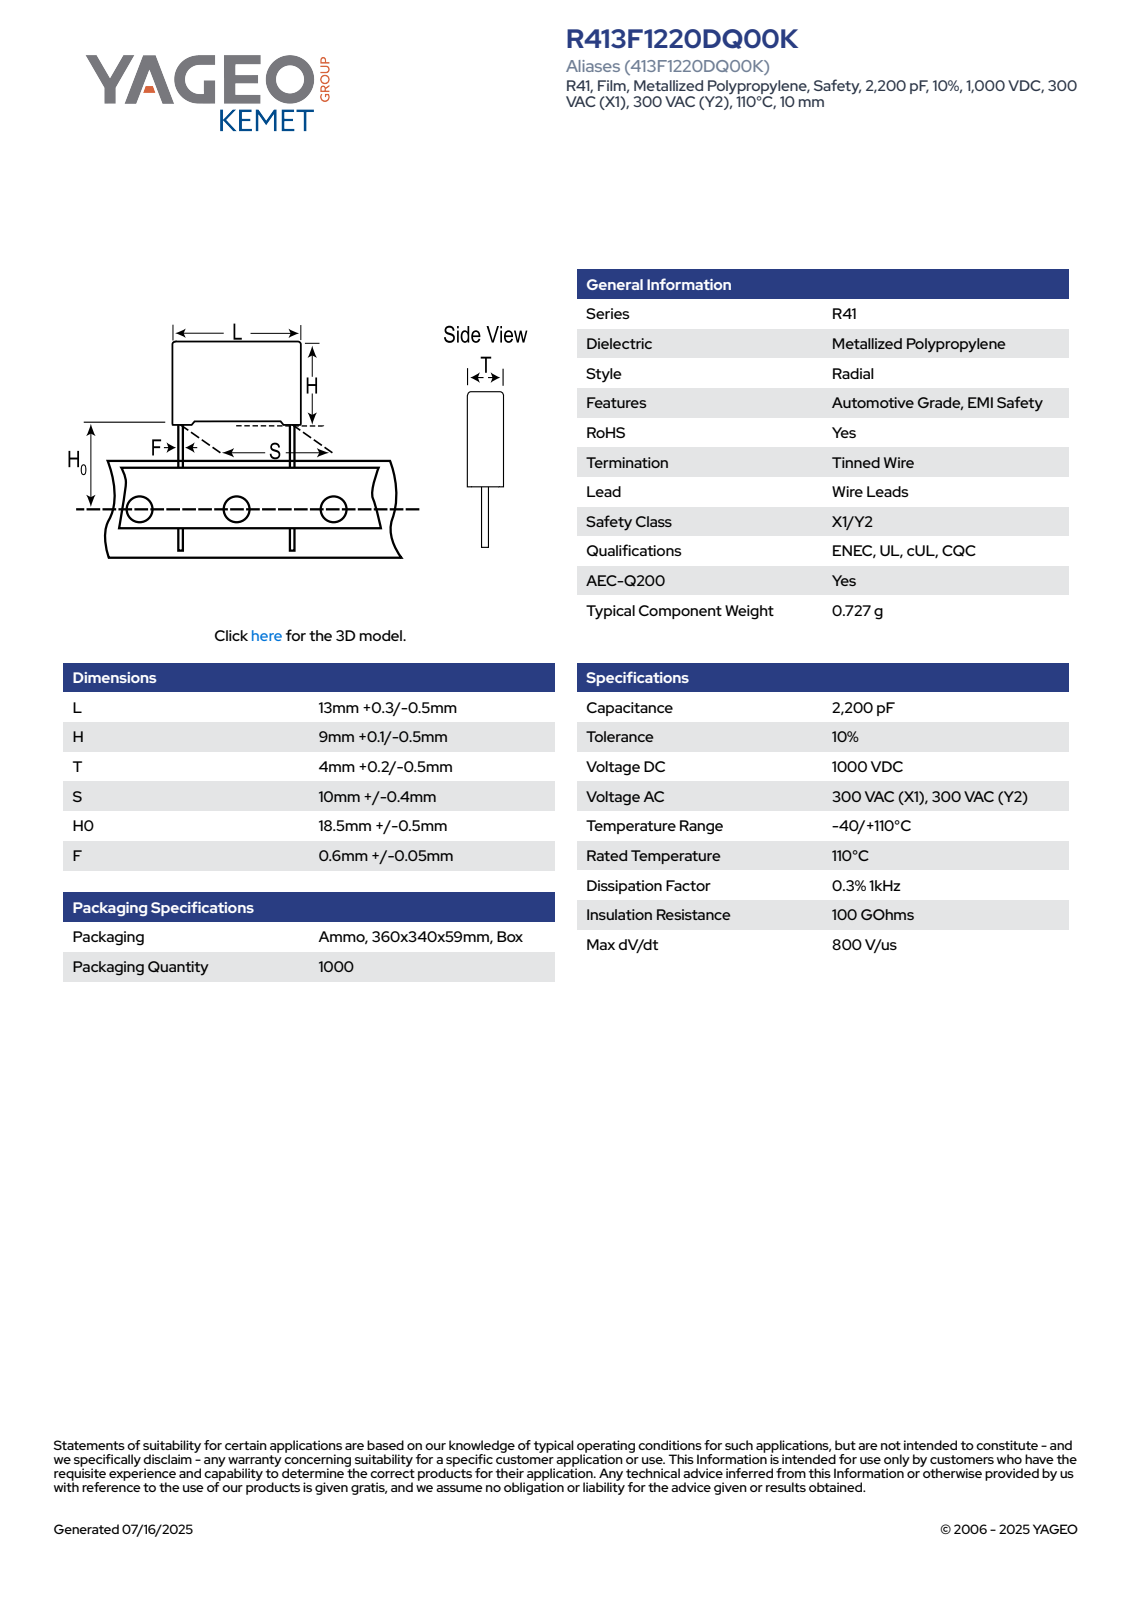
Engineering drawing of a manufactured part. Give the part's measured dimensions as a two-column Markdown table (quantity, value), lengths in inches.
| quantity | value |
| --- | --- |
| part name | CFR_RB2_13X9X4_L13.3H9.1T4.2S10H019F0.65 |
| STEP written by | SolidWorks 2020 (AUTOMOTIVE_DESIGN) |
| units | inches |
| bodies | 4 solids, 85 faces (77 planar, 8 cylindrical, 0 other) |
| overall size | 1.106 × 0.524 × 0.166 |
| volume | 0.03 in³ |
| surface area | 0.825 in² |
| round bosses / shafts (diameter × count) | 0.026 × 2 |
| partial cylindrical surfaces (radius × count) | 0.02 × 4 |
| main face-to-face distances | 0.165, 0.329, 0.524, 0.017, 0.148, 0.03, 0.358, 0.131, 0.012, 0.346 |
